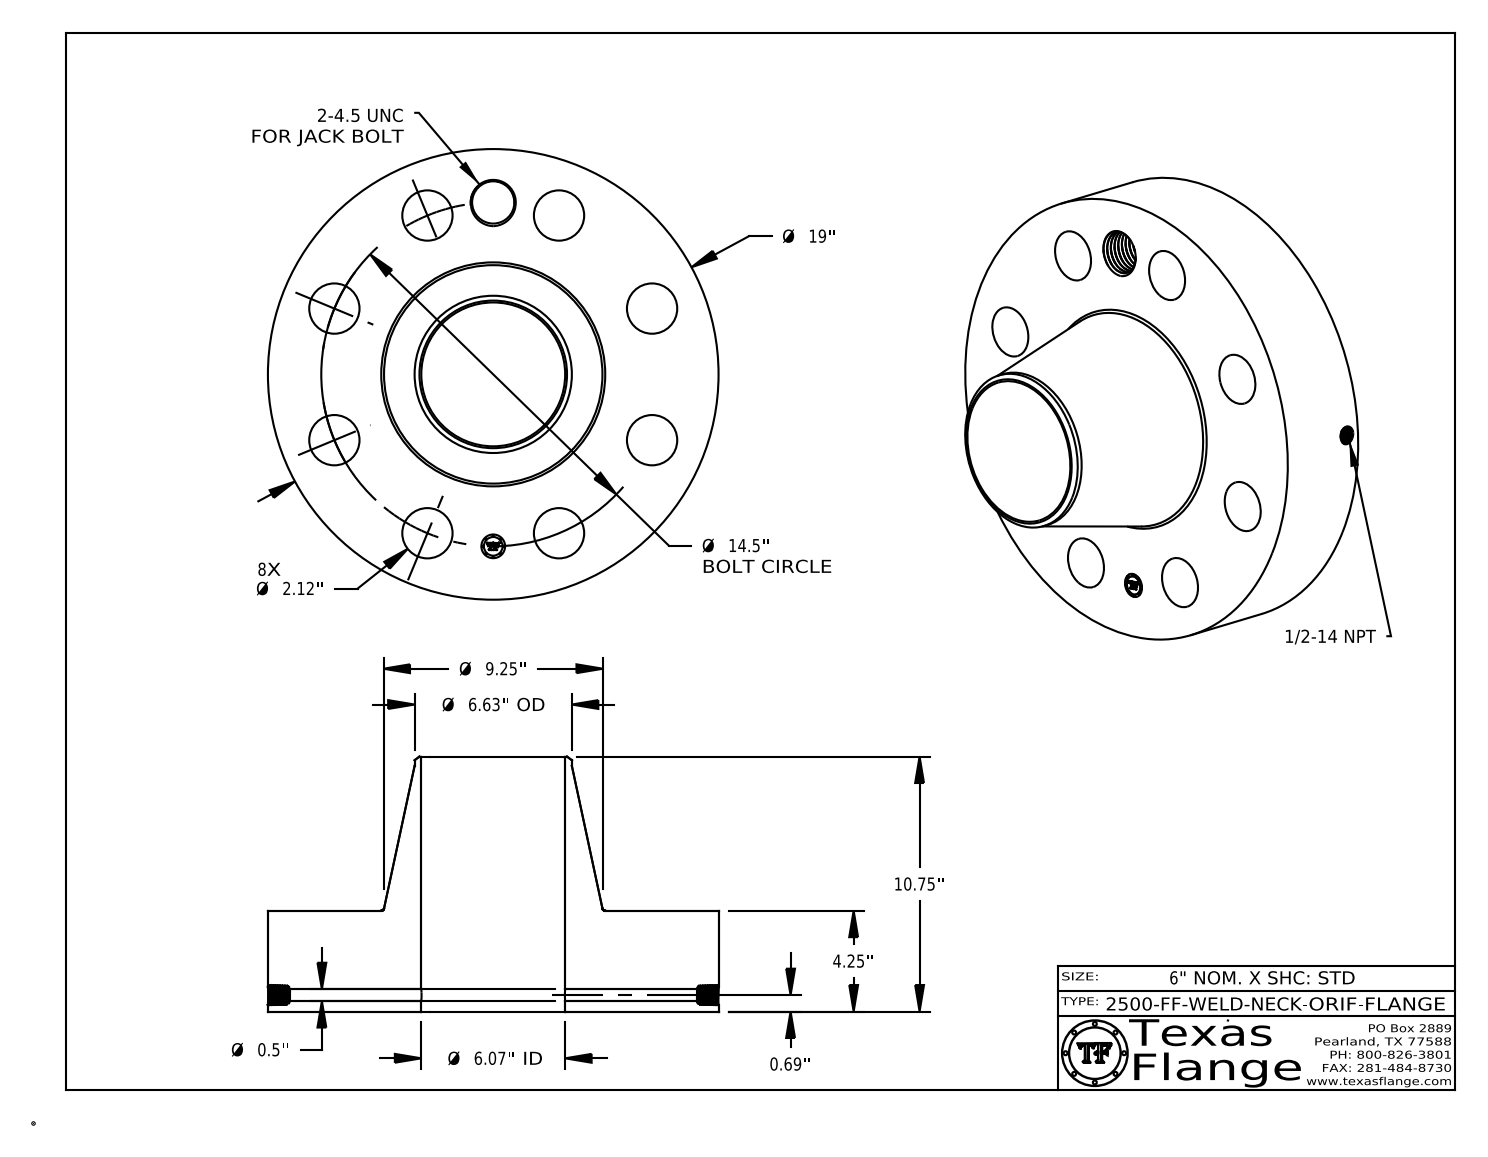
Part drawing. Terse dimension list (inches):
name: 2500-FF-WELD-NECK
written by: CATIA V5 STEP AP214 (AUTOMOTIVE_DESIGN)
unit: in
bodies: 1 solid, 791 faces (368 planar, 100 cylindrical, 323 other)
size: 19 × 19 × 10.75
volume: 1 078 in³; area: 1 320 in²
holes: 8× ⌀2.12, 1× ⌀0.5, 1× ⌀0.672, 1× ⌀1, 1× ⌀1.781, 1× ⌀6.065
bosses: 8× ⌀0.061, 1× ⌀19, 1× ⌀6.63, 1× ⌀0.788
face distances: 4.25, 10.75, 6.5, 4.235, 0.015, 6.515, 0.298, 0.293, 0.054, 0.248
hole spacings: 7.25, 5.549, 10.253, 13.396, 2.829, 8.056, 12.056, 14.221
